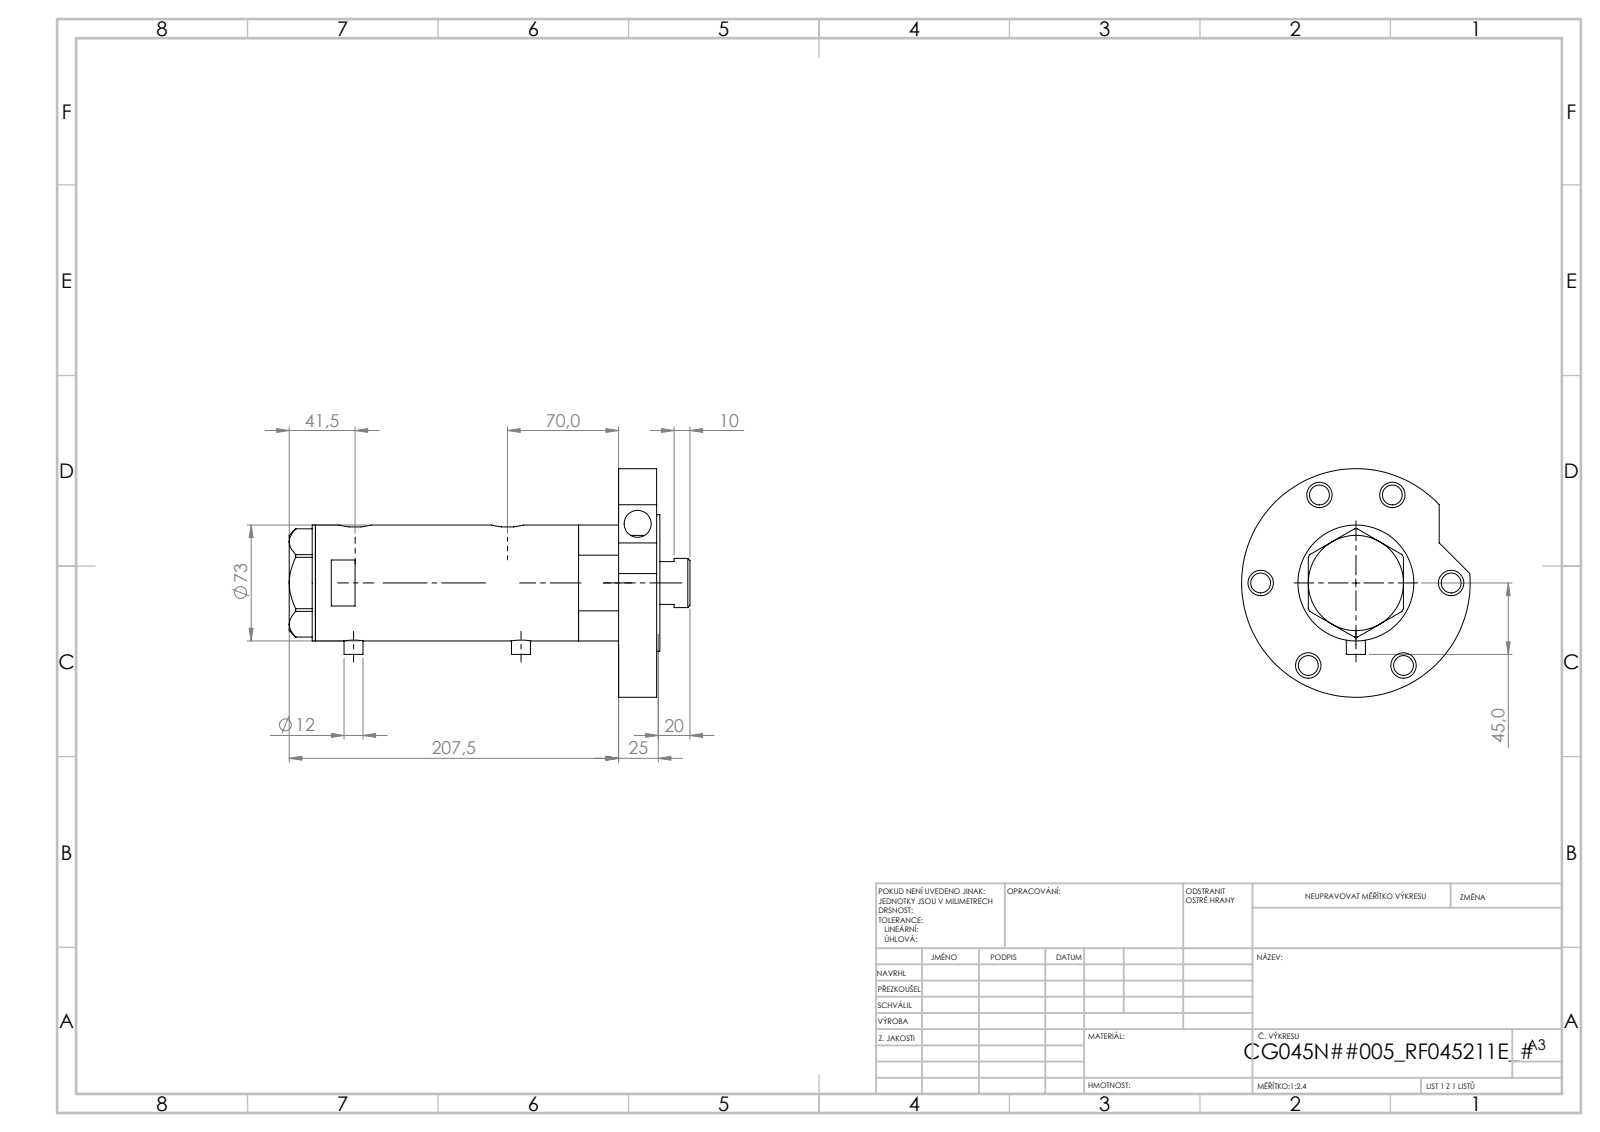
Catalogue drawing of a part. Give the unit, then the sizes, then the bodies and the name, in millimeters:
Units: millimetres
Overall size (bounding box): 196.52 × 144 × 144
Round holes (diameter × count): ⌀12.5 ×8, ⌀16 ×6, ⌀5 ×2, ⌀13.16 ×2, ⌀10.5 ×1, ⌀17 ×1, ⌀32 ×1, ⌀33.5 ×1, ⌀45 ×1, ⌀48 ×1, ⌀60 ×1, ⌀64 ×1
Round bosses / shafts (diameter × count): ⌀12 ×2, ⌀144 ×1, ⌀86 ×1, ⌀73 ×1, ⌀58 ×1, ⌀31 ×1
Partial cylindrical surfaces — rounded edges, fillets, slot ends (radius × count): R10 ×2
Main face-to-face distances: 24, 132.45, 26, 156.45, 2, 158.45, 106.45, 130.45, 16.49, 42.49
Hole centre spacings: 60, 56.65, 66.67, 99.77, 103.92, 107.62, 119.74, 0.99
Volume: 957 588 mm³ · Surface area: 174 807 mm²
Bodies: 5 solids, 169 faces (61 planar, 88 cylindrical, 20 other)
Part name (STEP PRODUCT): V270CG_RF211E; V270CG_FRONT; V270CG_MIDDLE; V270CG_BACK (+1 more)
STEP written by: SolidWorks 2019 (CONFIG_CONTROL_DESIGN)
